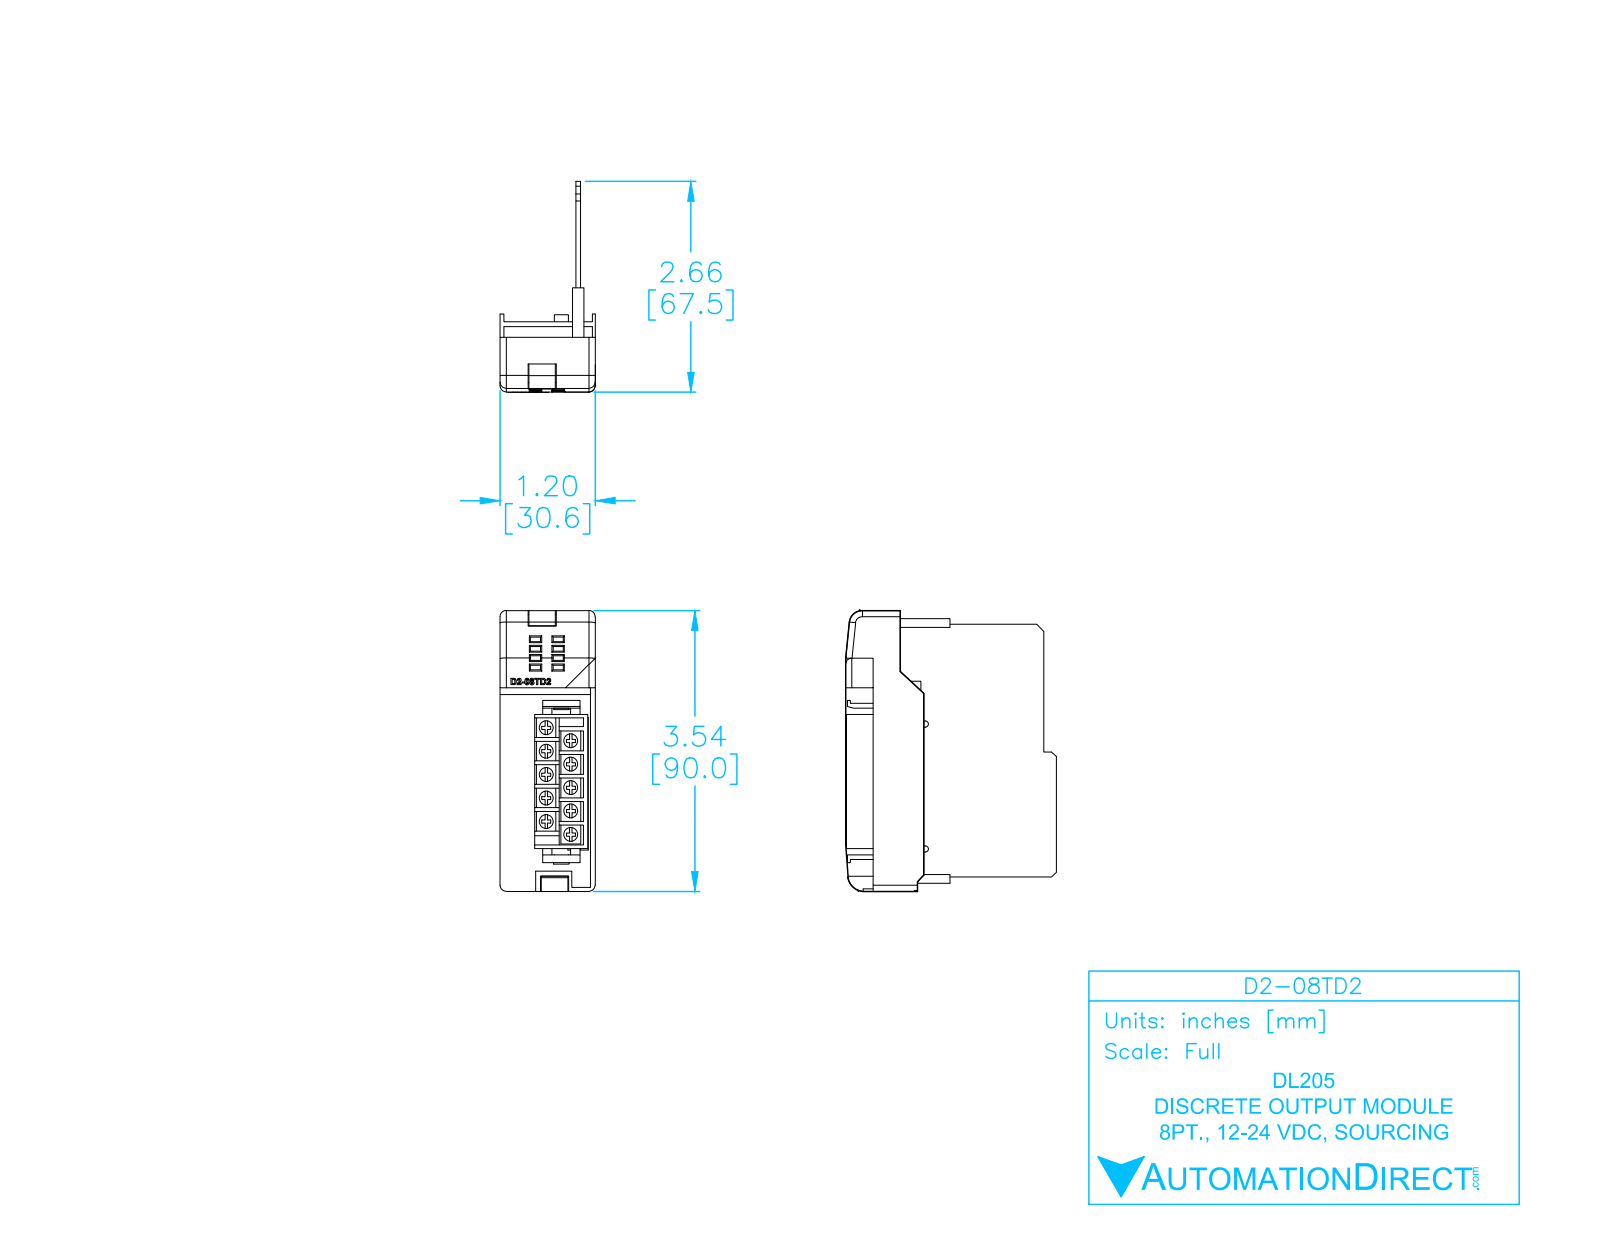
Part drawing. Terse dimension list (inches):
name: D2-08TD2_ModuleCase_light_NEW
written by: SolidWorks 2009 (AUTOMOTIVE_DESIGN)
unit: in
bodies: 6 solids, 584 faces (399 planar, 75 cylindrical, 110 other)
size: 3.543 × 2.66 × 1.203
volume: 1.548 in³; area: 44.22 in²
bosses: 10× ⌀0.177
rounds: 16× R0.014, 9× R0.079, 2× R0.01, 2× R0.039, 2× R0.049, 1× R0.162, 1× R0.212
face distances: 0.059, 0.186, 0.245, 0.093, 0.152, 0.093, 0.127, 0.033, 0.32, 0.956
